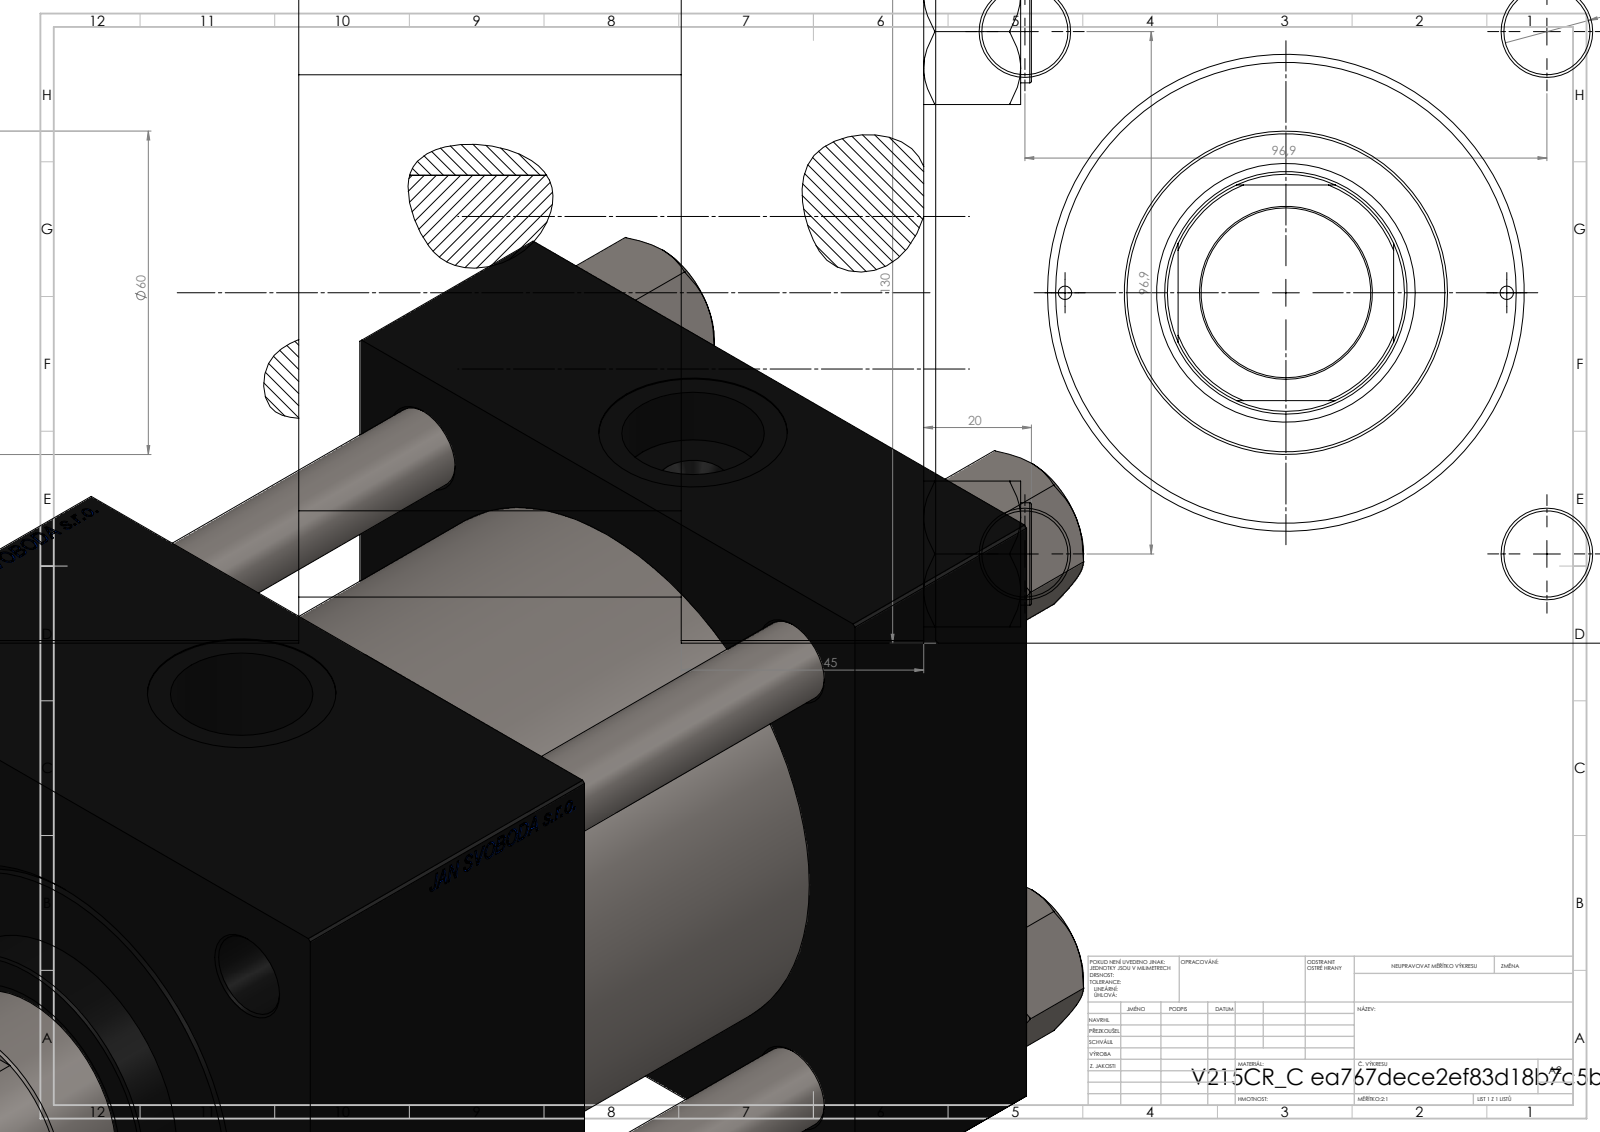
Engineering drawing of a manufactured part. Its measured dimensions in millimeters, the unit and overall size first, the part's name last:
Units: millimetres
Overall size (bounding box): 243 × 130 × 130
Round holes (diameter × count): ⌀16 ×4, ⌀2.5 ×2, ⌀7 ×2, ⌀26.44 ×2, ⌀35 ×2, ⌀31.5 ×1, ⌀45 ×1, ⌀48 ×1, ⌀76 ×1, ⌀85.5 ×1, ⌀100 ×1
Round bosses / shafts (diameter × count): ⌀19 ×4, ⌀106 ×1, ⌀60 ×1
Partial cylindrical surfaces — rounded edges, fillets, slot ends (radius × count): R22 ×1
Main face-to-face distances: 130, 45, 188, 143, 116, 71, 72, 20, 96, 51
Hole centre spacings: 49.02, 68.52, 96.9, 101.73, 41, 137.04, 82, 118.5
Volume: 2 425 000 mm³ · Surface area: 326 475 mm²
Bodies: 11 solids, 1203 faces (576 planar, 91 cylindrical, 536 other)
Part name (STEP PRODUCT): NUT_M5_C; V215CR_C_TYCINKA; V215CR_C_Body; V215CR_VCP_C (+1 more)
STEP written by: SolidWorks 2019 (CONFIG_CONTROL_DESIGN)
